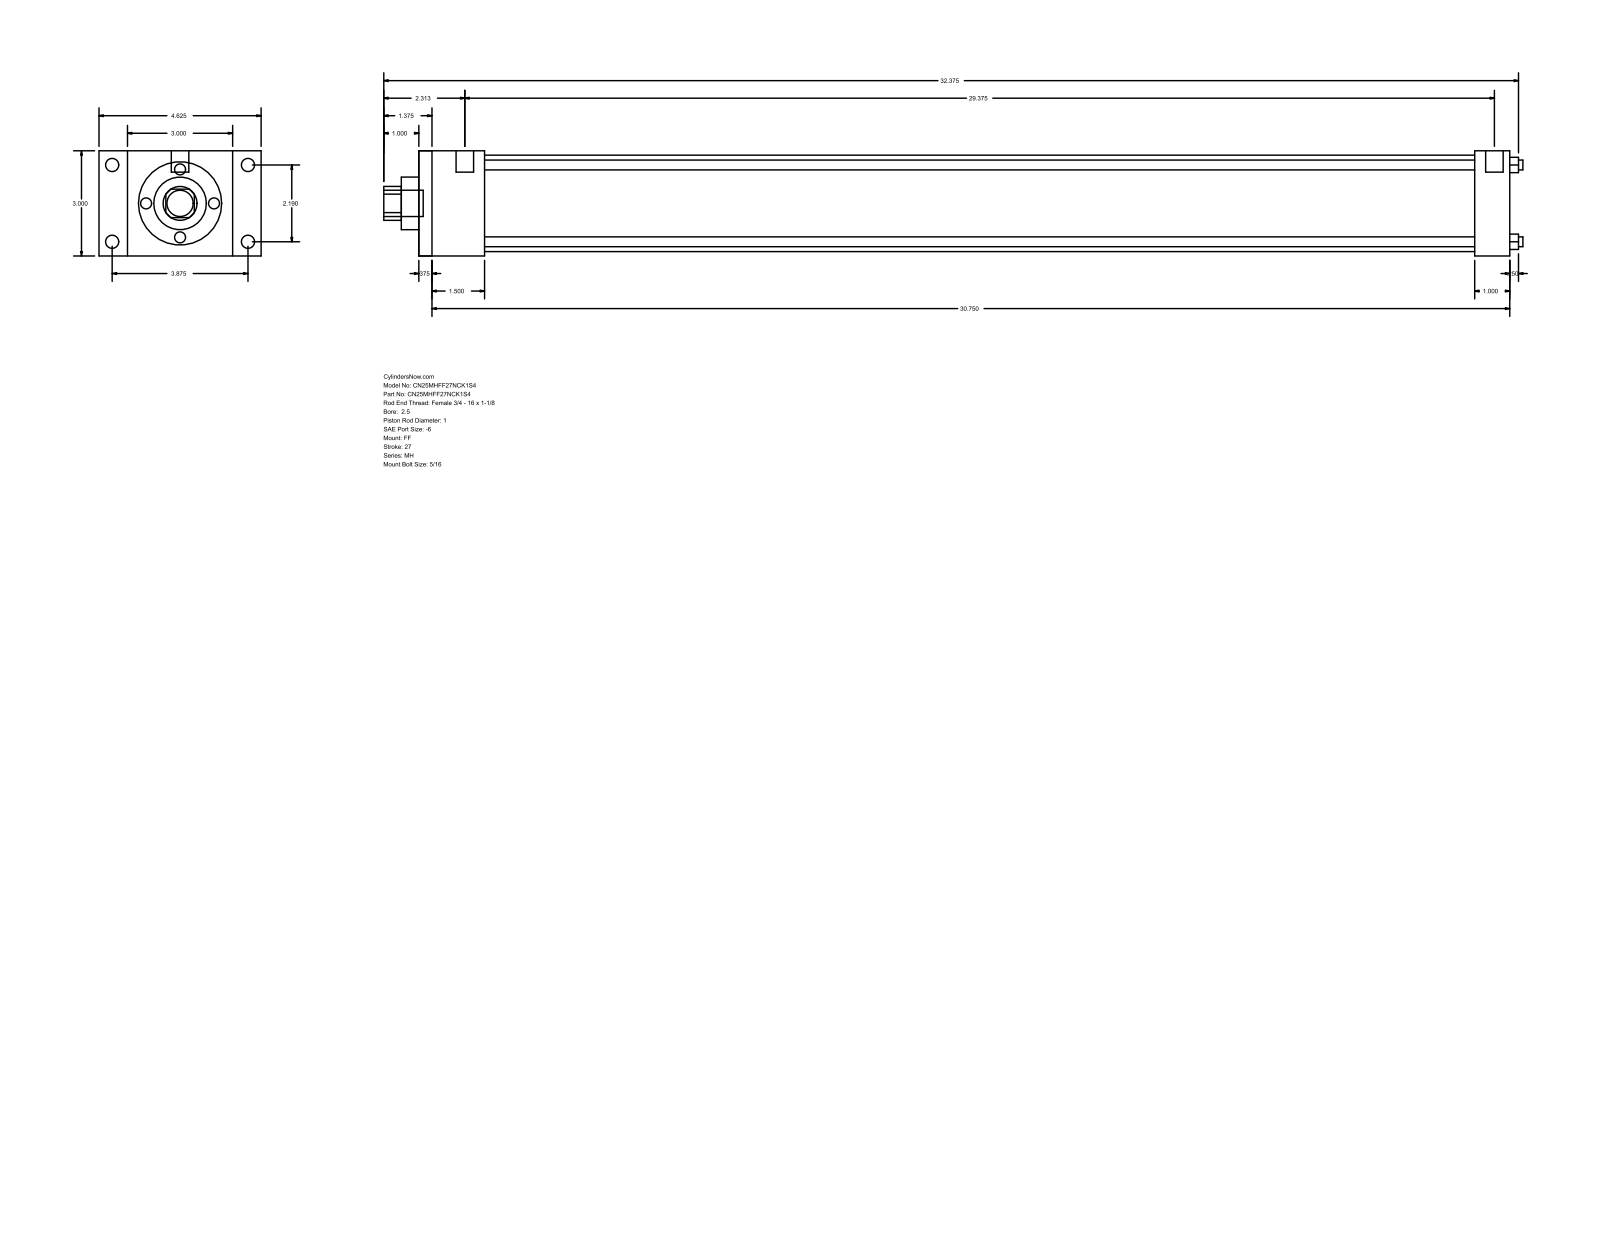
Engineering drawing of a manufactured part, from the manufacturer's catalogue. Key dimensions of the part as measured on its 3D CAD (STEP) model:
Part name (STEP PRODUCT): MH_FF__0250_1
STEP written by: GSSL Pune (CONFIG_CONTROL_DESIGN)
Units: millimetres
Bodies: 0 solids, 92 faces (64 planar, 28 cylindrical, 0 other)
Overall size (bounding box): 825.5 × 117.47 × 76.2
Round holes (diameter × count): ⌀7.14 ×4, ⌀25.4 ×1, ⌀38.1 ×1, ⌀69.85 ×1
Round bosses / shafts (diameter × count): ⌀9.53 ×4, ⌀5.56 ×4, ⌀12.7 ×2, ⌀19.05 ×1
Partial cylindrical surfaces — rounded edges, fillets, slot ends (radius × count): R12.29 ×1
Main face-to-face distances: 76.2, 790.58, 9.52, 781.06, 25.4, 47.63, 765.18, 38.11, 755.66, 717.55
Hole centre spacings: 39.33, 55.62, 78.66
